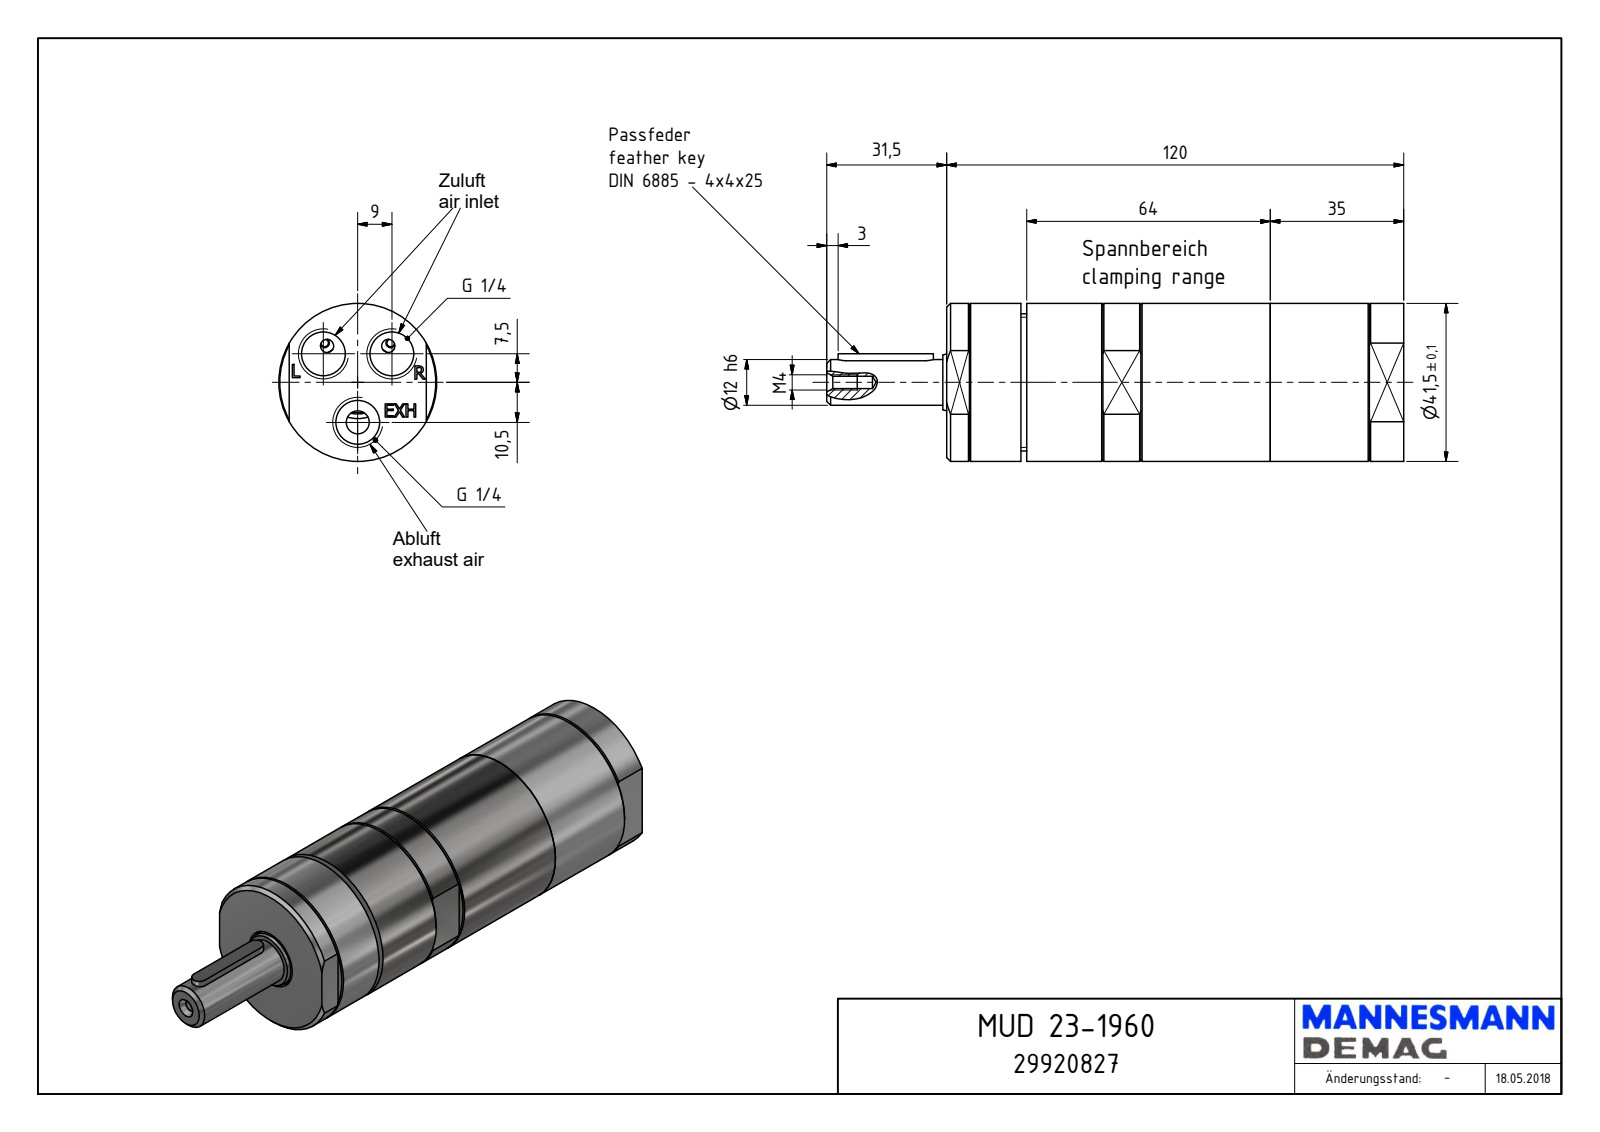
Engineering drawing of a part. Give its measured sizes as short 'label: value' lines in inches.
name: MUD 23-19360_29920827
written by: Autodesk Inventor 2018 (AUTOMOTIVE_DESIGN)
unit: in
bodies: 1 solid, 134 faces (86 planar, 20 cylindrical, 28 other)
size: 5.965 × 1.634 × 1.634
volume: 9.815 in³; area: 33.49 in²
holes: 3× ⌀0.451, 1× ⌀0.128, 1× ⌀0.63
bosses: 1× ⌀1.634, 1× ⌀1.417, 1× ⌀0.589, 1× ⌀0.472
rounds: 2× R0.079
face distances: 4.724, 0.039, 0.827, 1.457, 0.768, 3.957, 0.059, 3.898, 4.325, 3.557
hole spacings: 0.461, 0.792, 0.413, 0.709
